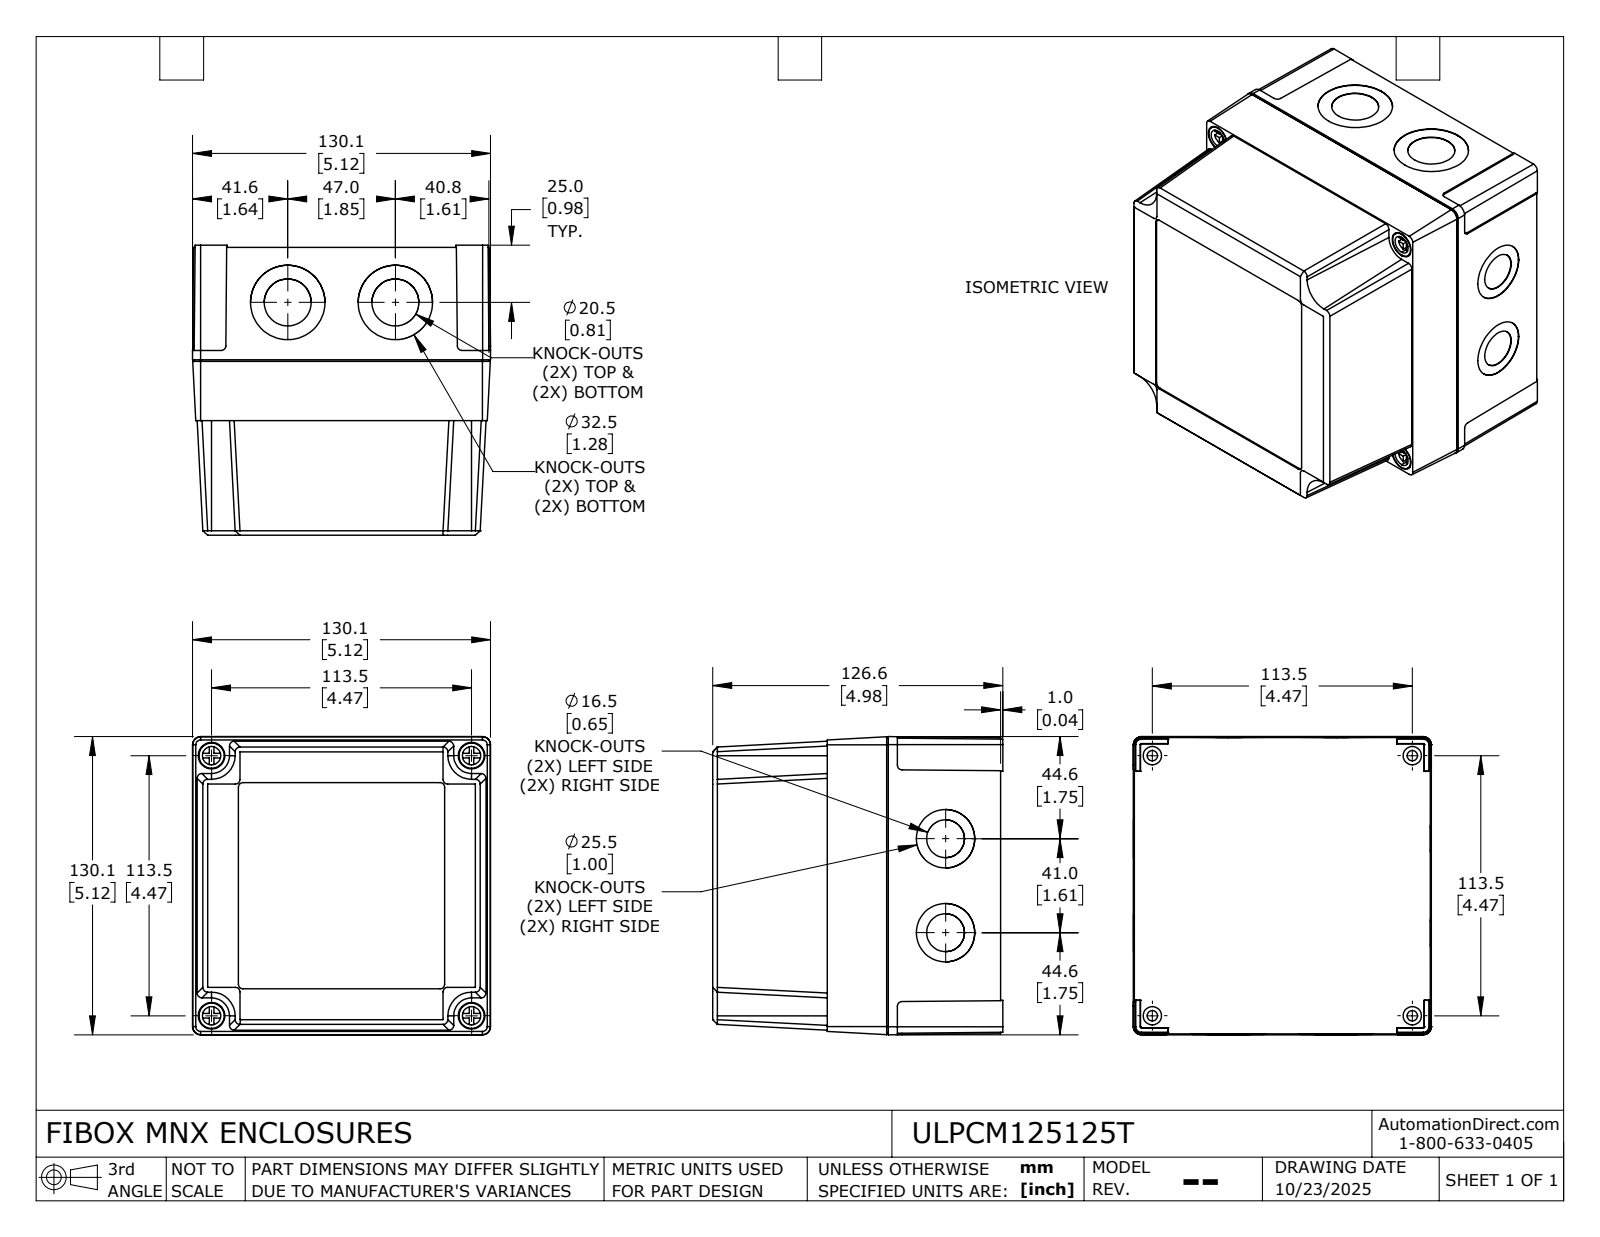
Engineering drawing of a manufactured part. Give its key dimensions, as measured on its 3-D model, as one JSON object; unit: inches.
{"part_name": "ULPCM125125T_Default", "step_written_by": "SolidWorks 2024 (CONFIG_CONTROL_DESIGN)", "units": "inches", "bodies": {"solids": 6, "faces": 577, "planar": 335, "cylindrical": 192, "other": 50}, "overall_size": [5.122, 5.122, 4.984], "volume_in3": 17.1, "surface_area_in2": 308.2, "round_holes": [[0.126, 8], [0.157, 8], [0.177, 4], [0.315, 4], [0.457, 4], [0.65, 4], [0.807, 4], [1.004, 4], [1.28, 4]], "round_bosses_or_shafts": [[0.315, 8], [0.098, 8], [0.433, 4], [0.283, 4]], "partial_cylinders_radius": [[0.079, 8], [0.083, 8], [0.056, 6], [0.021, 4], [0.197, 4], [0.023, 2]], "face_to_face_distances": [0.055, 0.165, 0.118, 4.854, 4.736, 0.078, 0.022, 4.925, 4.807, 0.071], "hole_center_spacings": [2.281, 4.587, 0.888, 1.476, 1.796, 2.506, 3.543, 3.7]}
